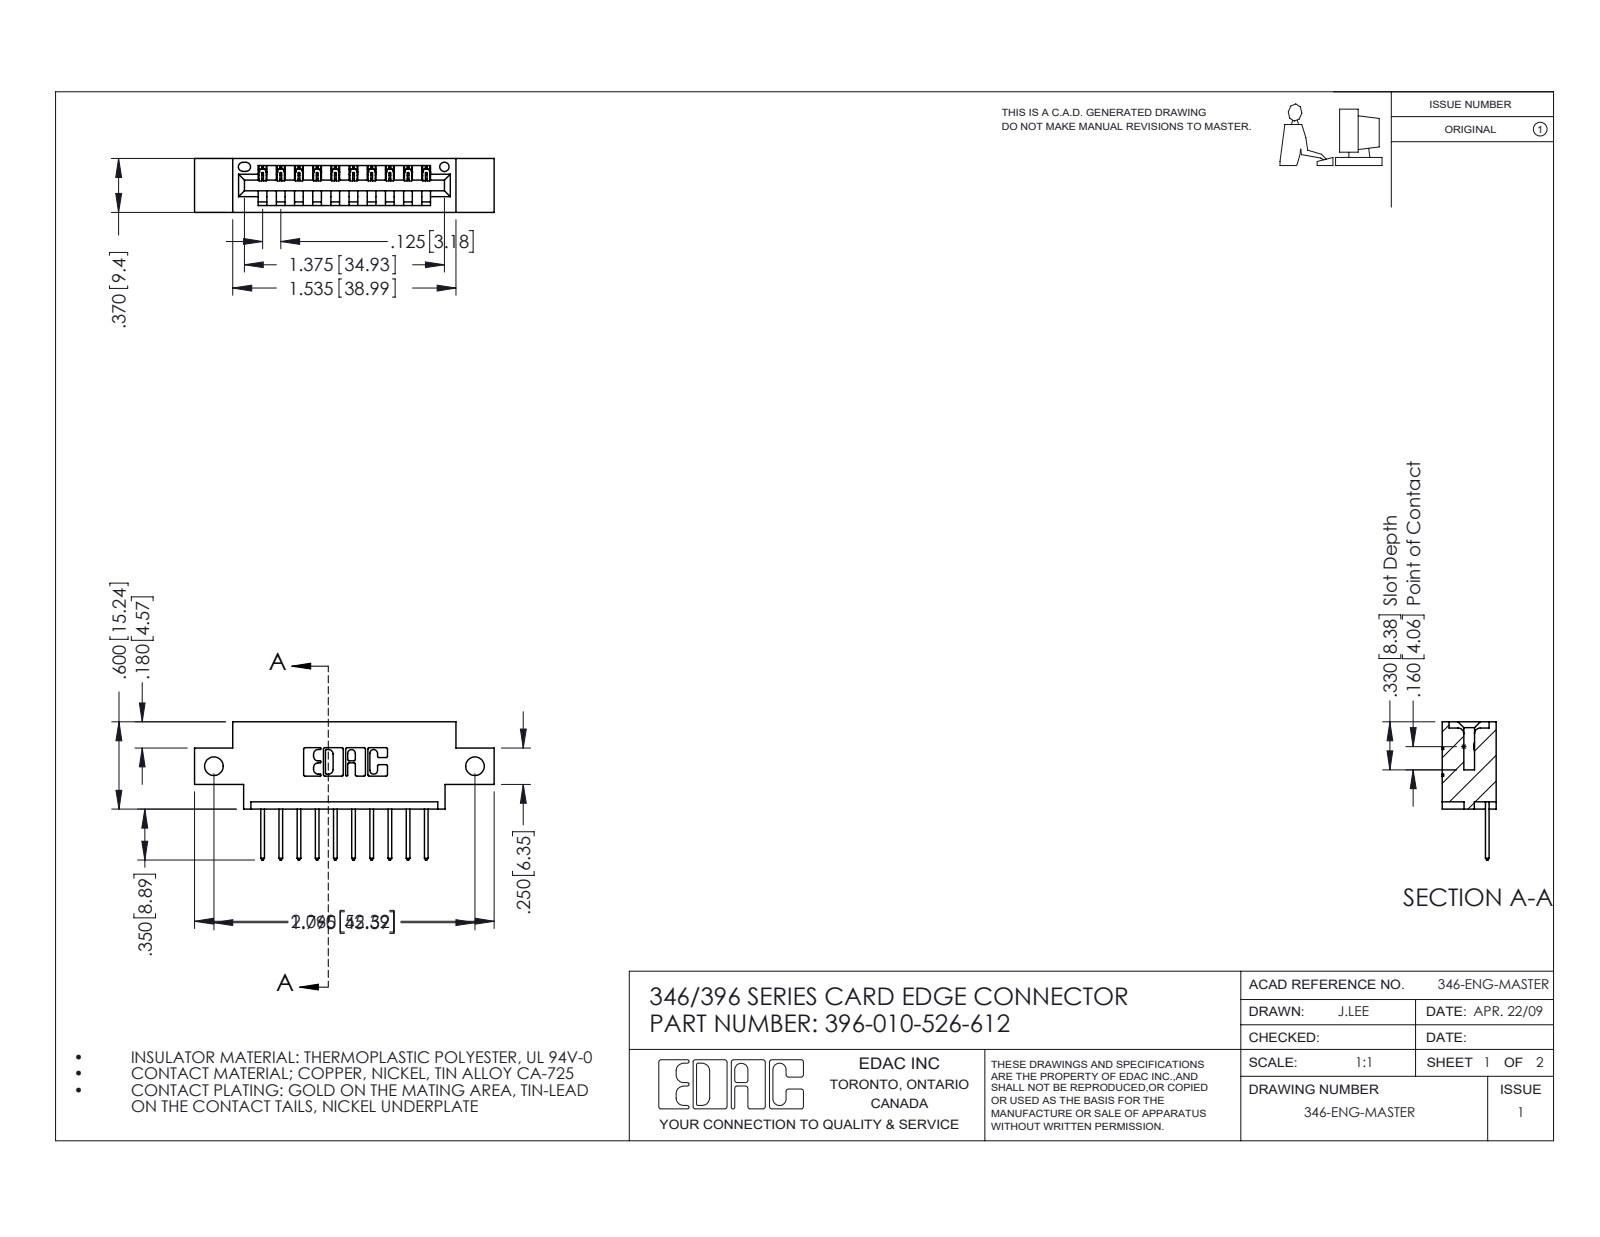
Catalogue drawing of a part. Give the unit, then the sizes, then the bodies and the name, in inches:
Units: inches
Overall size (bounding box): 2.06 × 0.95 × 0.37
Round holes (diameter × count): ⌀0.128 ×2, ⌀0.064 ×1
Partial cylindrical surfaces — rounded edges, fillets, slot ends (radius × count): R0.01 ×22, R0.006 ×20, R0.01 ×20, R0.007 ×6, R0.031 ×6, R0.026 ×3, R0.031 ×2, R0.04 ×2
Main face-to-face distances: 0.25, 0.37, 0.048, 0.322, 0.072, 0.298, 0.025, 0.148, 0.222, 0.1
Hole centre spacings: 1.795
Volume: 0.277 in³ · Surface area: 8.264 in²
Bodies: 11 solids, 706 faces (480 planar, 226 cylindrical, 0 other)
Part name (STEP PRODUCT): 396-010-526-612; 345-292-001_345-293-126; 346 Part_0.170 Offset - Side Mount
STEP written by: SolidWorks 2016 (CONFIG_CONTROL_DESIGN)
